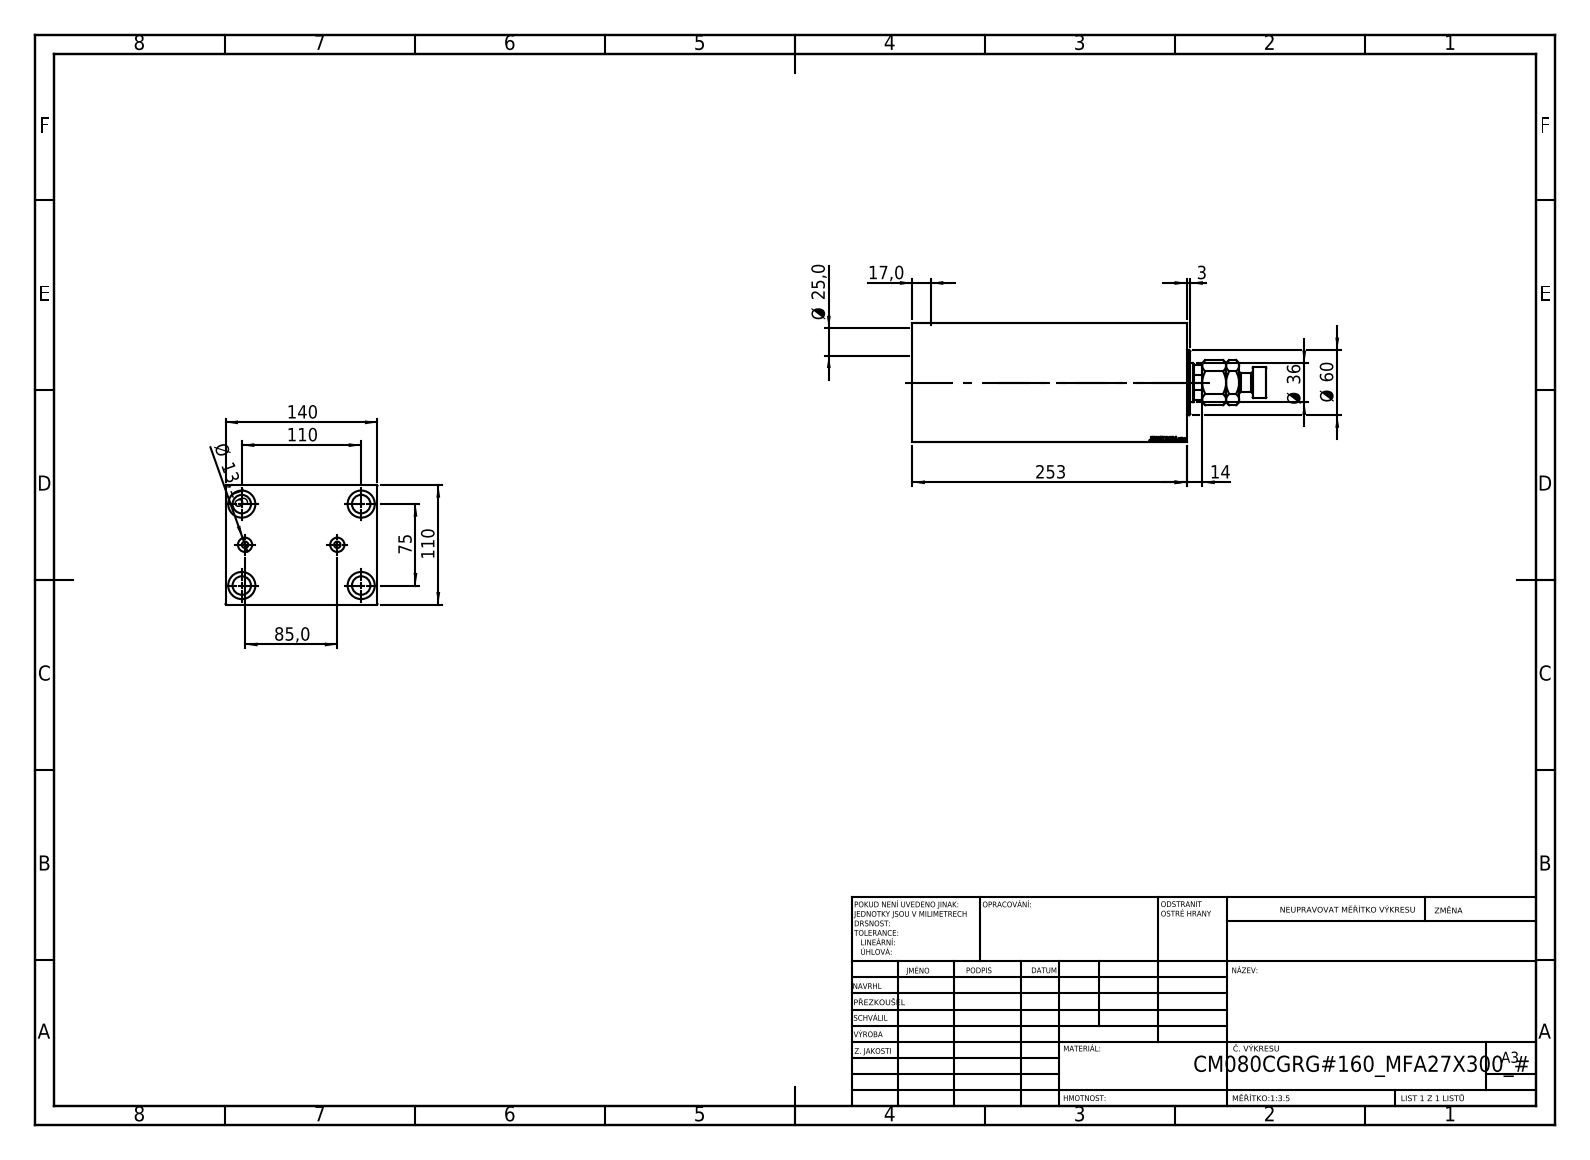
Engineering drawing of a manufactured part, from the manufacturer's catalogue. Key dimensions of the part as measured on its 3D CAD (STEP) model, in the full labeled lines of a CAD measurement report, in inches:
Part name (STEP PRODUCT): V450CM_C_VCP; V450CM_VC_B; MFA; V450CM_C_Body
STEP written by: SolidWorks 2019 (CONFIG_CONTROL_DESIGN)
Units: inches
Bodies: 4 solids, 912 faces (424 planar, 62 cylindrical, 426 other)
Overall size (bounding box): 12.835 × 5.512 × 4.331
Volume: 184.8 in³ · Surface area: 542.1 in²
Round holes (diameter × count): ⌀0.669 ×4, ⌀0.984 ×4, ⌀0.236 ×2, ⌀0.518 ×2, ⌀1.004 ×1, ⌀1.417 ×1, ⌀1.555 ×1, ⌀3.15 ×1, ⌀3.228 ×1, ⌀3.425 ×1
Round bosses / shafts (diameter × count): ⌀2.362 ×1, ⌀1.102 ×1, ⌀0.709 ×1
Partial cylindrical surfaces — rounded edges, fillets, slot ends (radius × count): R0.689 ×1
Main face-to-face distances: 4.331, 5.512, 9.961, 9.134, 0.827, 0.551, 9.409, 8.583, 6.85, 6.299
Hole centre spacings: 2.621, 1.481, 1.712, 2.953, 3.766, 4.331, 4.464, 5.242
